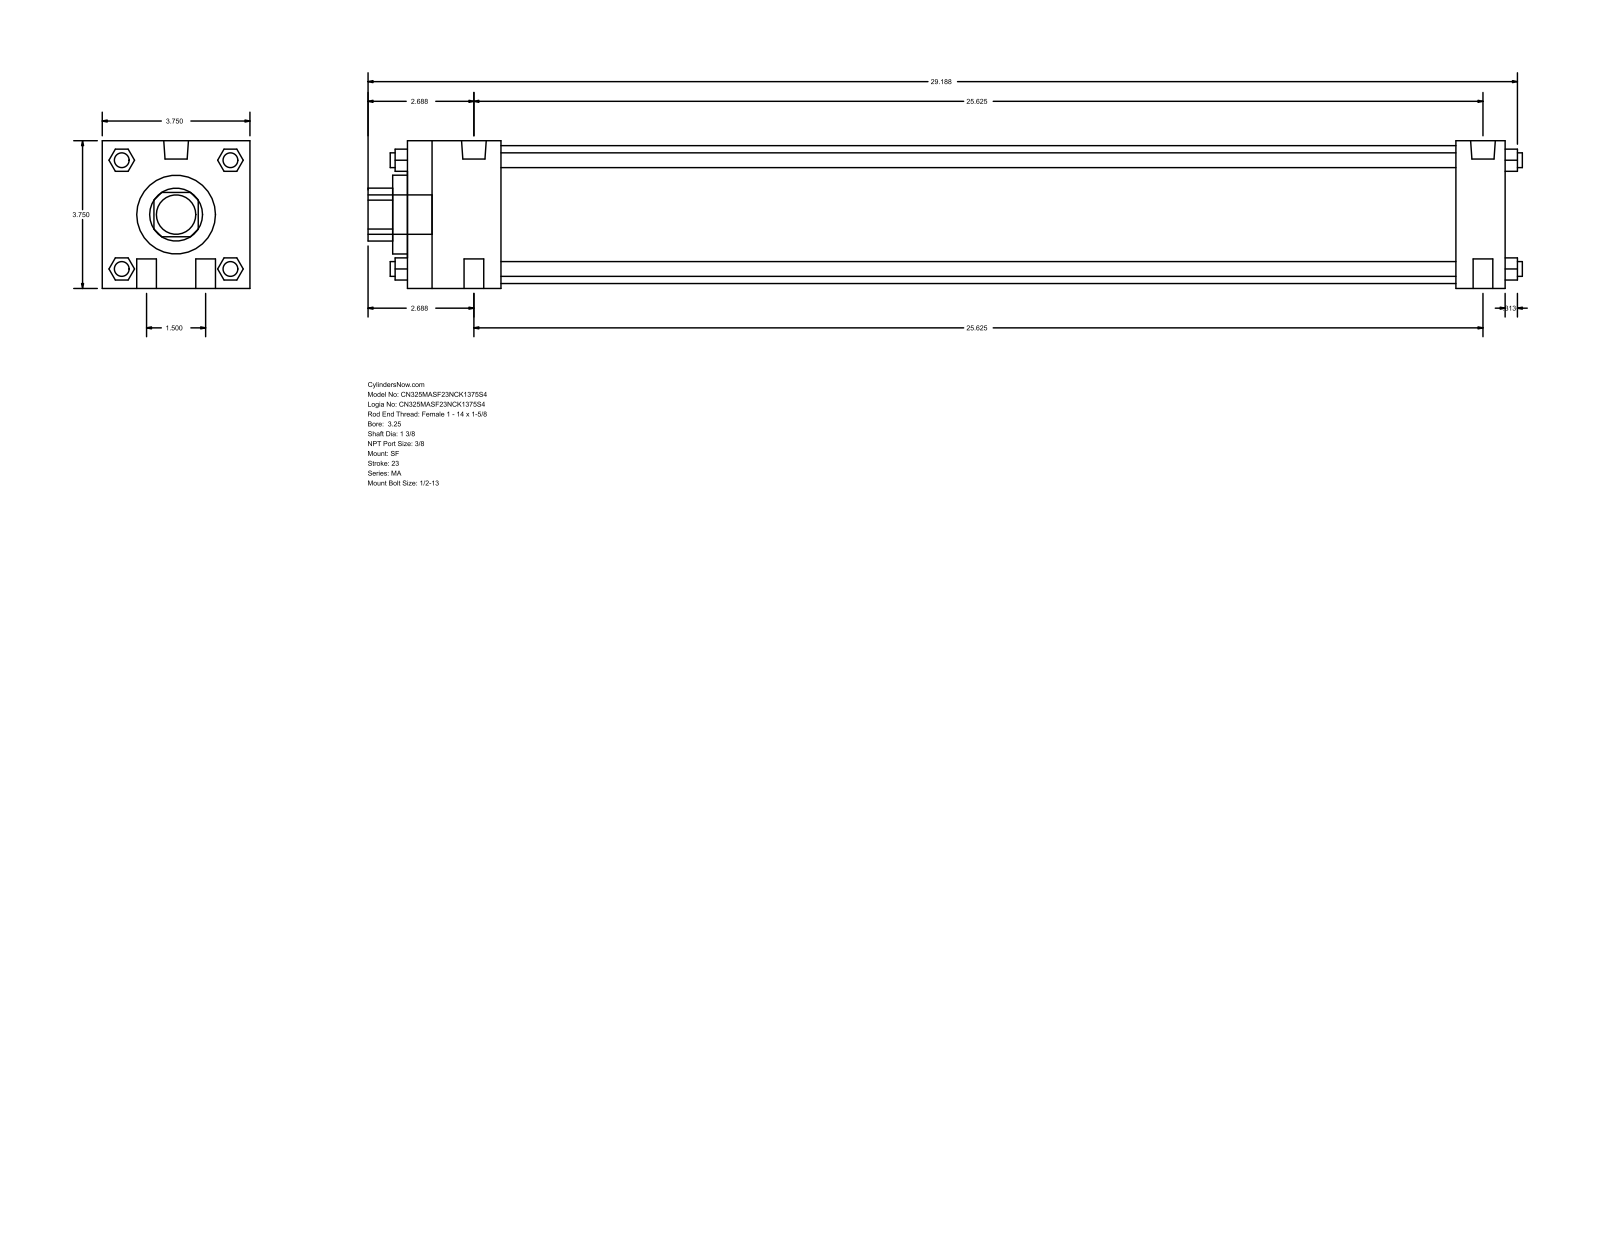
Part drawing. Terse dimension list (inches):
name: MA_SF__0325_1.375
written by: GSSL Pune (CONFIG_CONTROL_DESIGN)
unit: in
bodies: 0 solids, 124 faces (94 planar, 30 cylindrical, 0 other)
size: 29.313 × 3.75 × 3.75
holes: 1× ⌀1.375, 1× ⌀2, 1× ⌀3.5
bosses: 4× ⌀0.5, 4× ⌀0.375, 2× ⌀0.627, 2× ⌀0.437, 1× ⌀1
rounds: 1× R0.672
face distances: 3.75, 27.875, 26.625, 1.25, 2.375, 24.25, 25.5, 0.375, 2.75, 27
